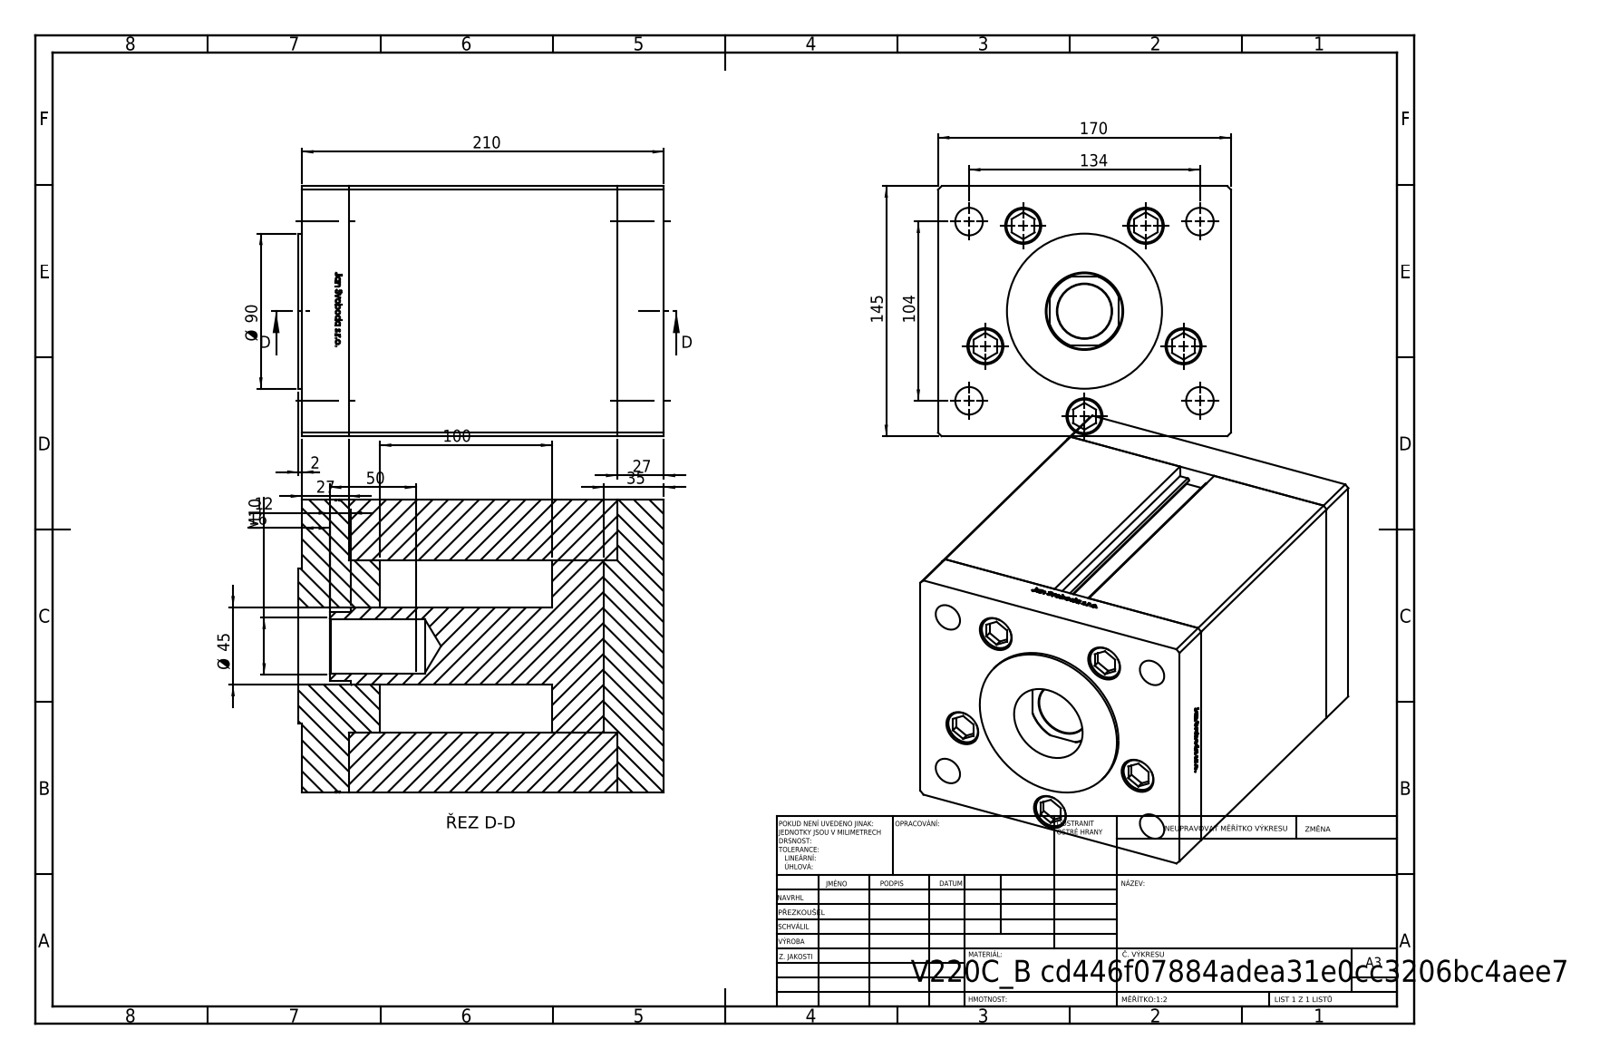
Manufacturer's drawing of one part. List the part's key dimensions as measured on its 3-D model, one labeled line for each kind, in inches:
Part name (STEP PRODUCT): V220C BACK_B; V220C_VC_B; V220C_FRONT_B; ALLEN BOLT (+1 more)
STEP written by: SolidWorks 2019 (CONFIG_CONTROL_DESIGN)
Units: inches
Bodies: 14 solids, 1185 faces (464 planar, 147 cylindrical, 574 other)
Overall size (bounding box): 8.346 × 6.693 × 5.709
Volume: 264.2 in³ · Surface area: 654 in²
Round holes (diameter × count): ⌀0.689 ×5, ⌀0.827 ×5, ⌀0.63 ×4, ⌀0.079 ×2, ⌀0.518 ×2, ⌀1.24 ×1, ⌀1.772 ×1
Round bosses / shafts (diameter × count): ⌀0.315 ×5, ⌀3.937 ×1, ⌀3.543 ×1
Partial cylindrical surfaces — rounded edges, fillets, slot ends (radius × count): R0.037 ×2, R0.866 ×1
Main face-to-face distances: 1.063, 7.205, 5.709, 6.142, 6.693, 0.307, 8.268, 1.37, 5.835, 6.898
Hole centre spacings: 2.402, 3.339, 1.241, 1.302, 2.661, 2.773, 2.872, 2.884
